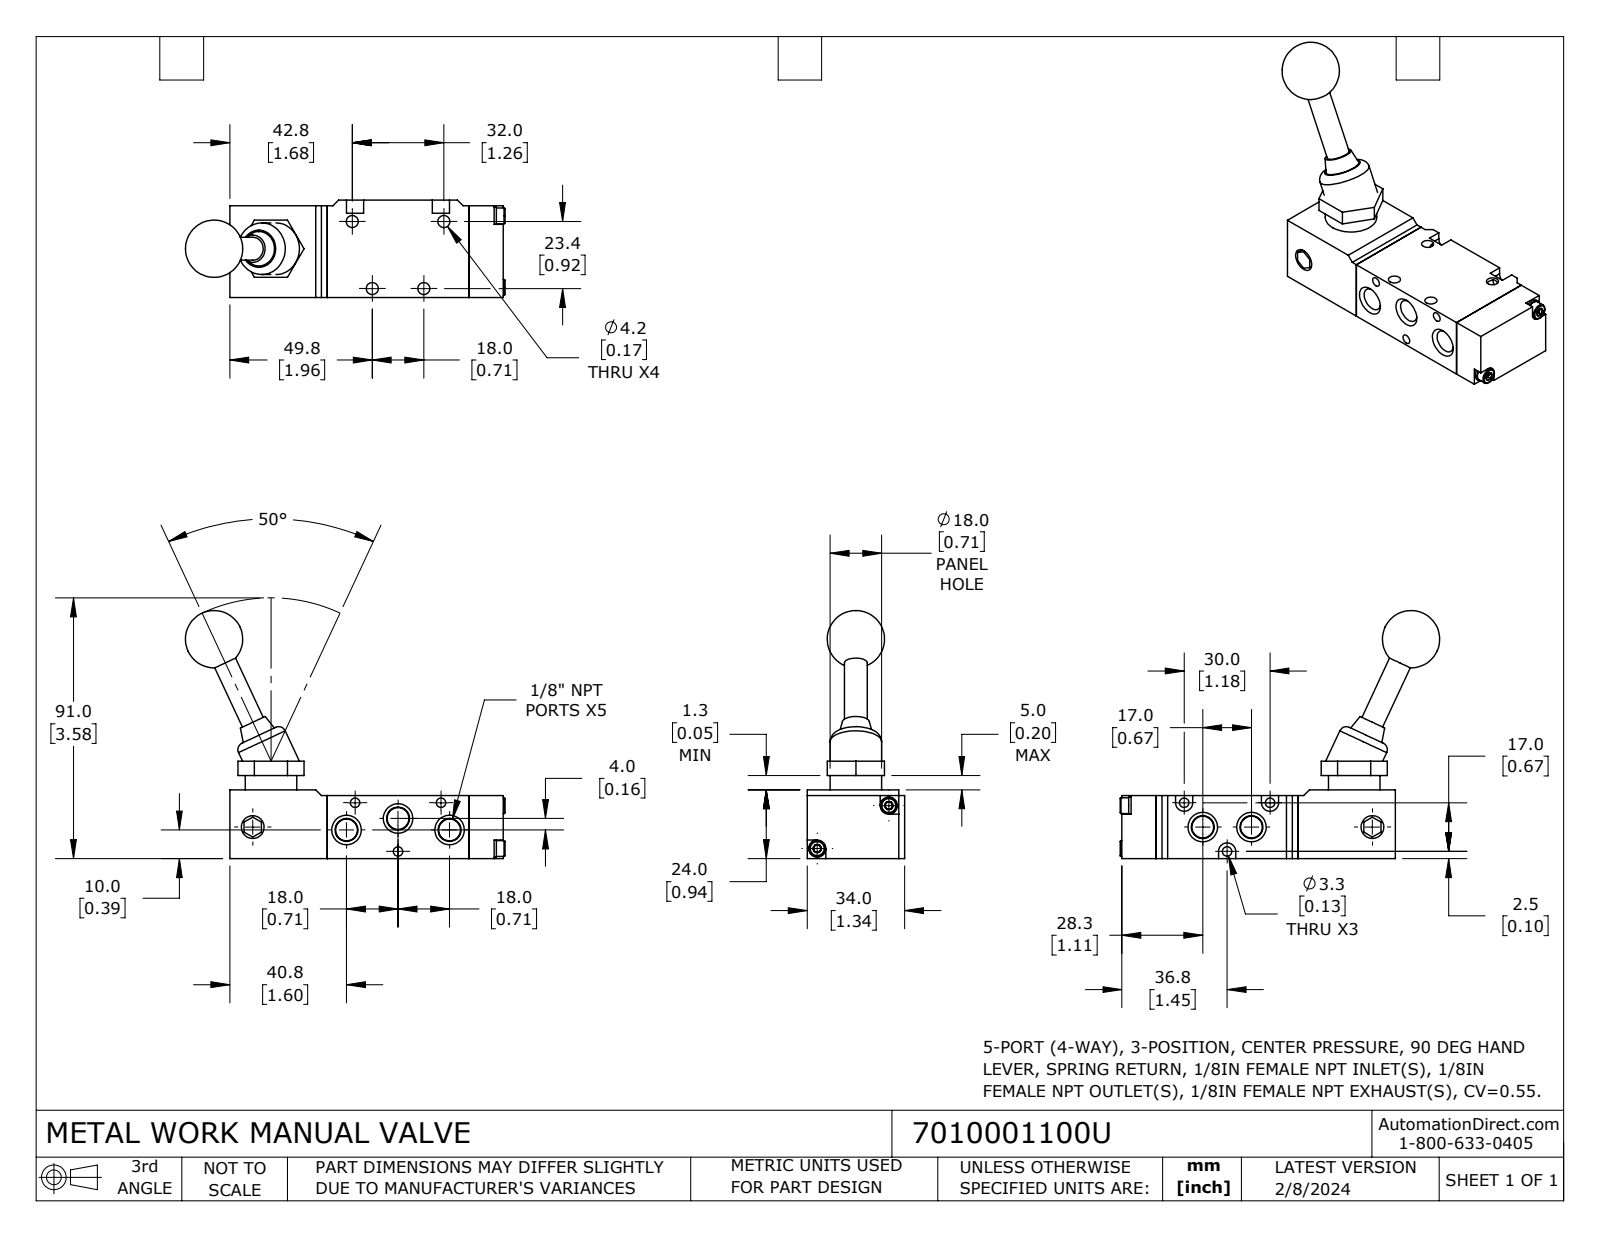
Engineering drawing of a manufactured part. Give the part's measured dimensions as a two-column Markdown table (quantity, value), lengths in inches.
| quantity | value |
| --- | --- |
| part name | 7010001100U |
| STEP written by | SolidWorks 2023 (CONFIG_CONTROL_DESIGN) |
| units | inches |
| bodies | 8 solids, 208 faces (105 planar, 49 cylindrical, 54 other) |
| overall size | 4.393 × 3.409 × 1.339 |
| volume | 4.828 in³ |
| surface area | 34.88 in² |
| round holes (diameter × count) | 0.165 × 4, 0.13 × 3, 0.118 × 2, 0.313 × 1 |
| round bosses / shafts (diameter × count) | 0.709 × 2, 0.236 × 2, 0.217 × 2, 0.315 × 1 |
| partial cylindrical surfaces (radius × count) | 0.118 × 3 |
| main face-to-face distances | 0.866, 1.339, 1.949, 0.079, 1.26, 0.472, 3.287, 0.945, 2.421, 3.76 |
| hole center spacings | 0.893, 0.961, 1.348, 0.709, 1.148, 1.181, 1.26, 1.447 |
